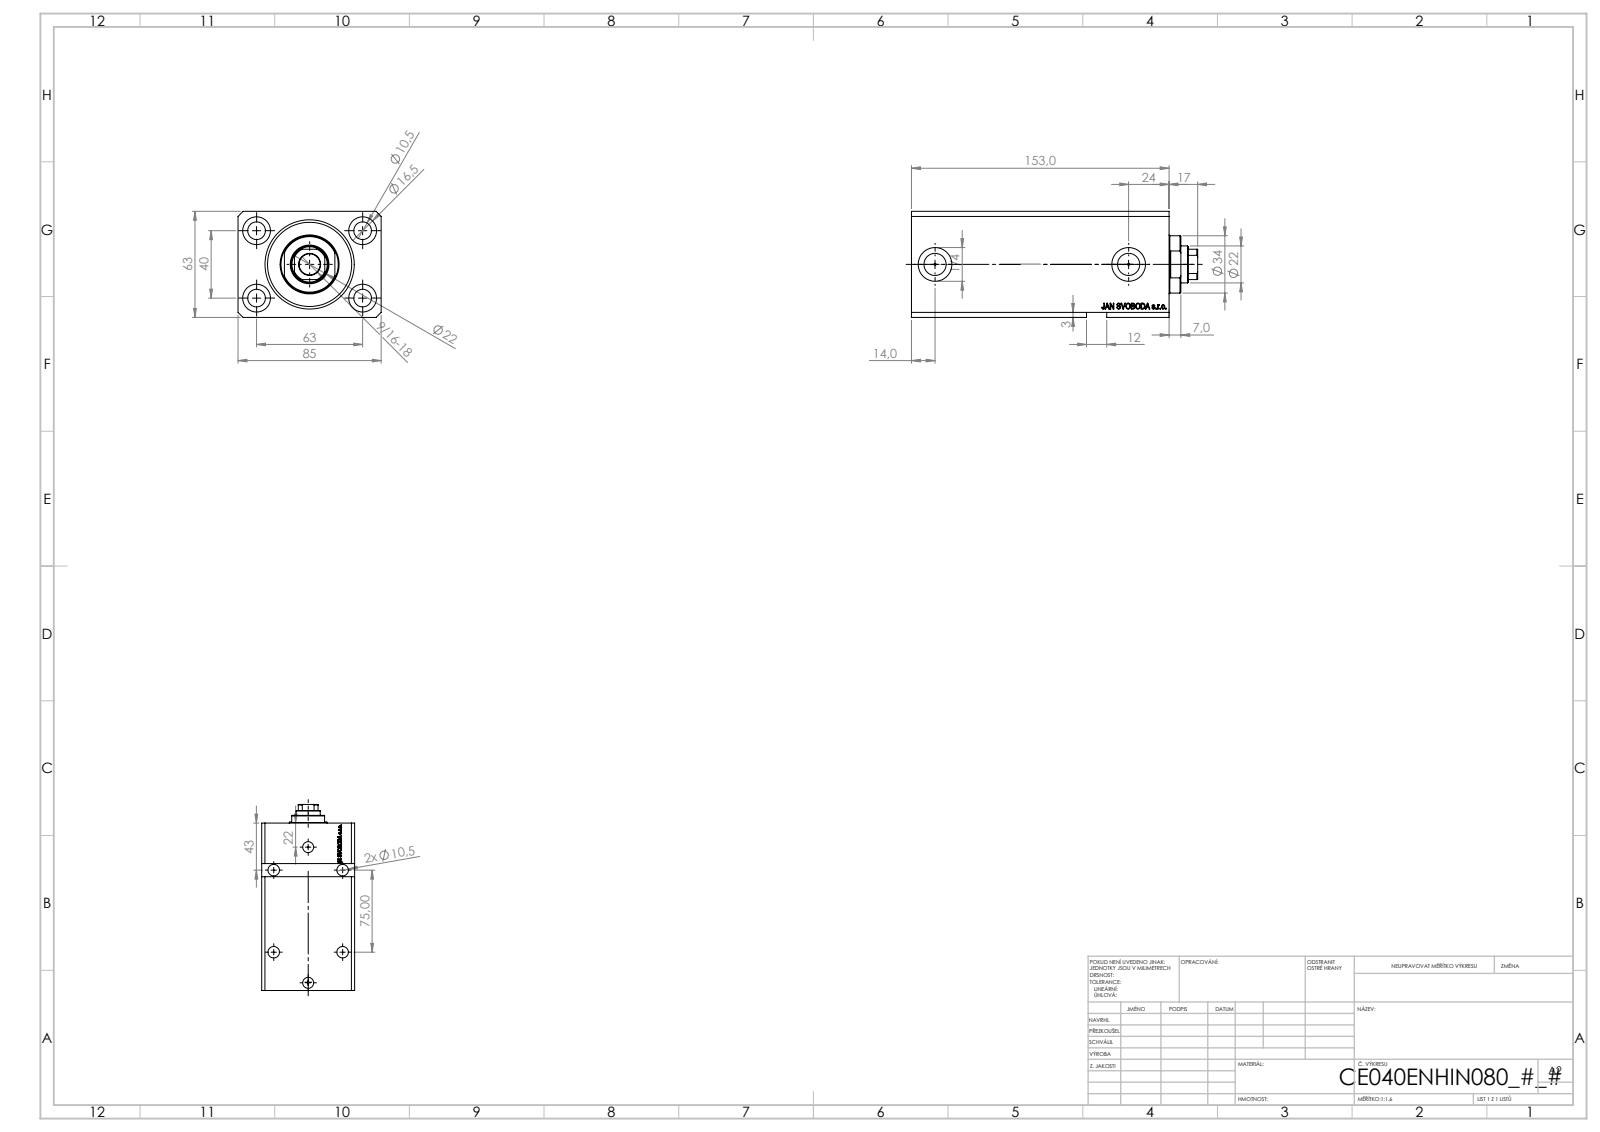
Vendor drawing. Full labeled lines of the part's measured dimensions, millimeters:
Part name (STEP PRODUCT): V250CE_VC_E; V250CE_C_VCP; V250CE_E_Body
STEP written by: SolidWorks 2019 (CONFIG_CONTROL_DESIGN)
Units: millimetres
Bodies: 3 solids, 937 faces (459 planar, 104 cylindrical, 374 other)
Overall size (bounding box): 170 × 85 × 63
Volume: 666 198 mm³ · Surface area: 126 235 mm²
Round holes (diameter × count): ⌀10.5 ×8, ⌀1.25 ×4, ⌀16.5 ×4, ⌀10 ×2, ⌀13.16 ×2, ⌀20 ×2, ⌀12.5 ×1, ⌀22 ×1, ⌀40 ×1, ⌀53 ×1
Round bosses / shafts (diameter × count): ⌀34 ×1
Partial cylindrical surfaces — rounded edges, fillets, slot ends (radius × count): R10.5 ×1
Main face-to-face distances: 63, 85, 153, 17, 136, 11.4, 124.6, 141.6, 56, 60
Hole centre spacings: 37.31, 63, 37.86, 40, 41.8, 42.15, 74.63, 75
